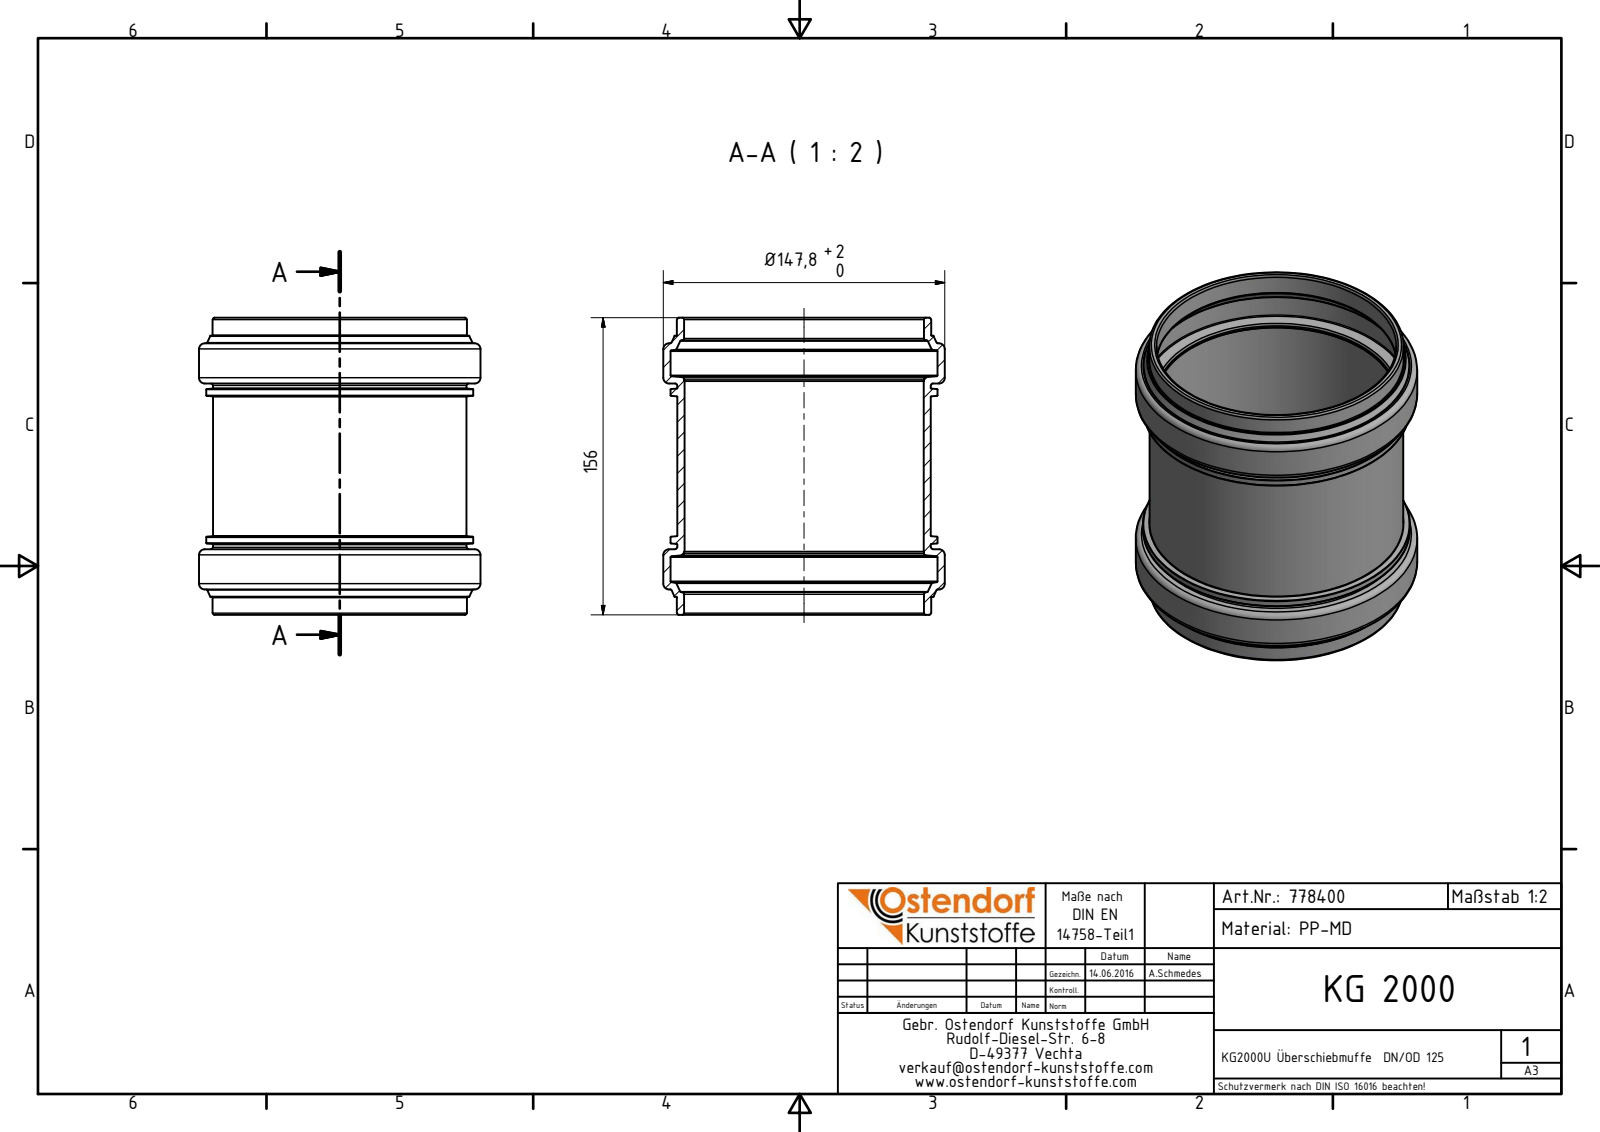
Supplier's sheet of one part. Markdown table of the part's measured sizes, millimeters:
| quantity | value |
| --- | --- |
| part name | 778400 KG2000U Überschiebmuffe DN_OD 125 |
| STEP written by | Autodesk Inventor 2016 (AUTOMOTIVE_DESIGN) |
| units | millimeters |
| bodies | 1 solid, 76 faces (10 planar, 16 cylindrical, 50 other) |
| overall size | 156 × 147.8 × 147.8 |
| volume | 292 695 mm³ |
| surface area | 155 392 mm² |
| round holes (diameter × count) | 125.6 × 1, 125.9 × 1, 140.2 × 1 |
| round bosses / shafts (diameter × count) | 147.8 × 1, 133.5 × 1, 133.2 × 1 |
| main face-to-face distances | 34.5, 121.5, 87, 156, 13.4, 142.6, 21.1, 108.1, 9.48, 146.52 |
